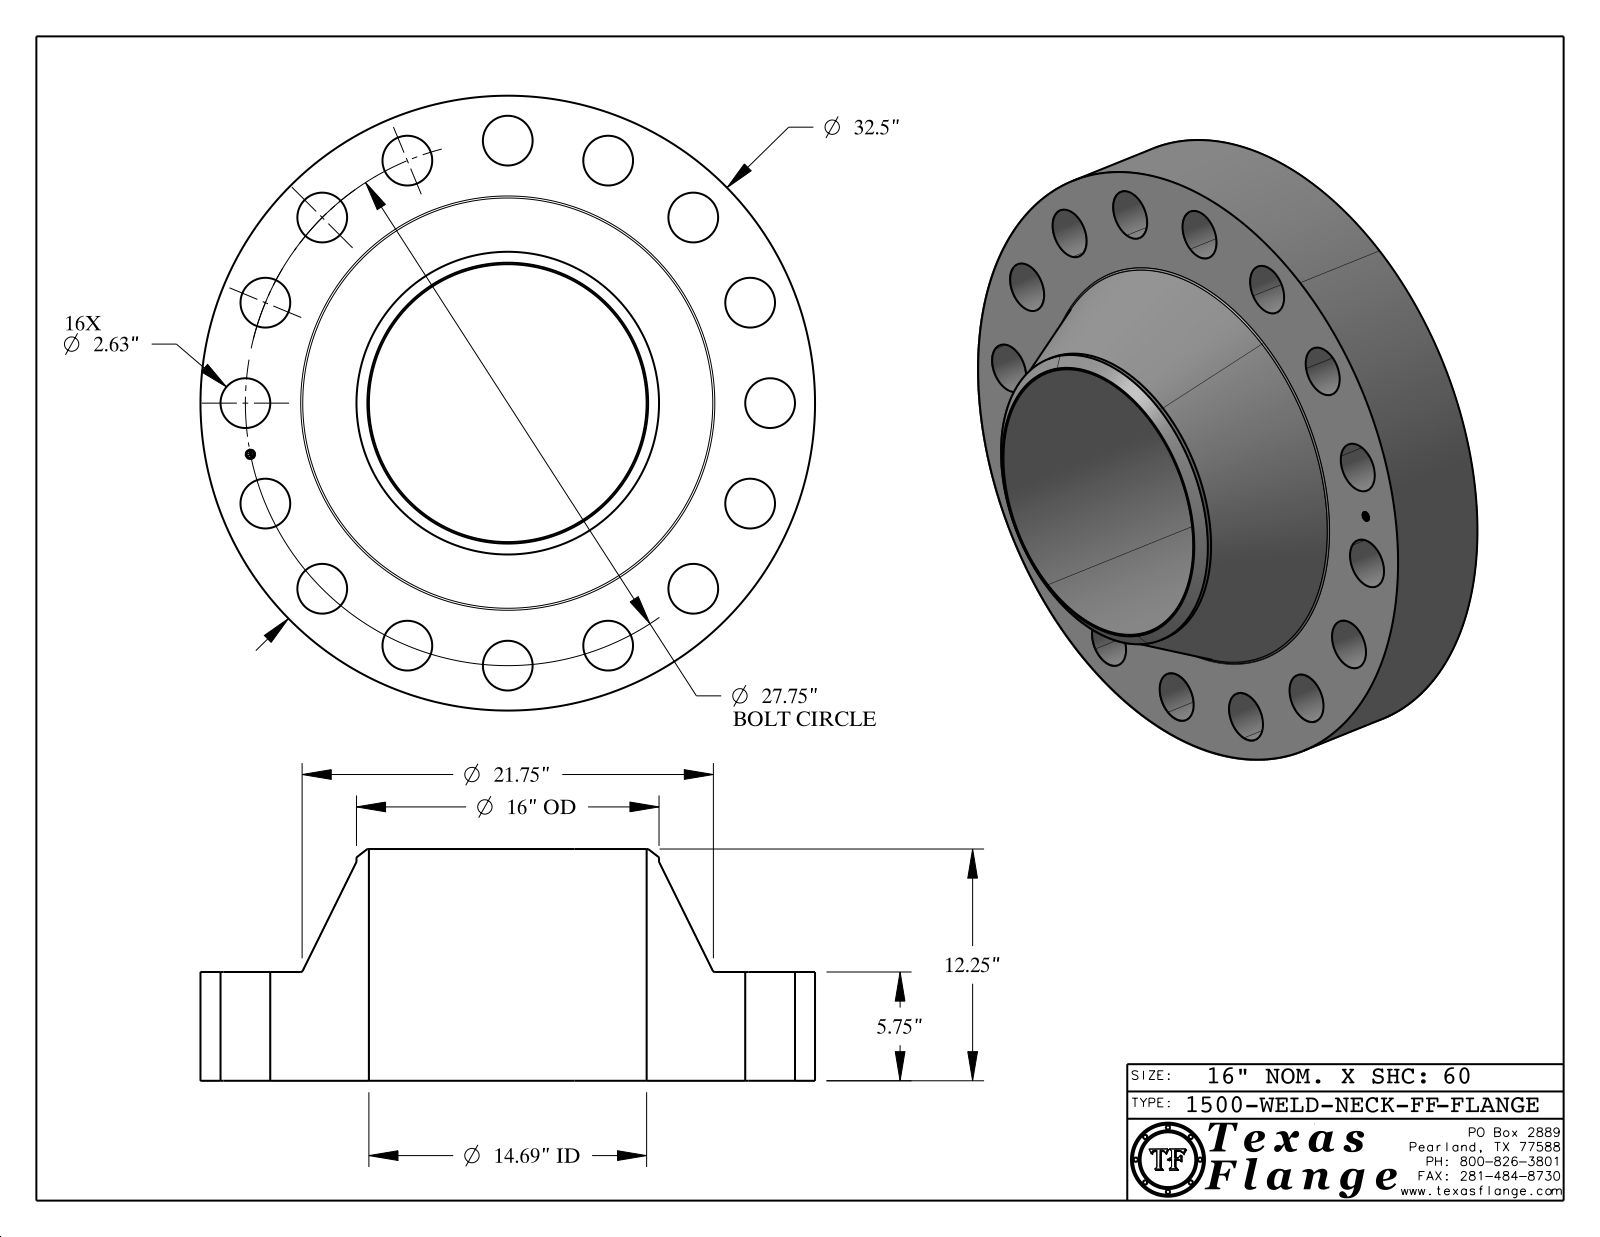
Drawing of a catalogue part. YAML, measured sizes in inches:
part_name: "1500-WELD-NECK-FF"
step_written_by: "CATIA V5 STEP AP214 (AUTOMOTIVE_DESIGN)"
units: inches
bodies: {solids: 1, faces: 432, planar: 368, cylindrical: 58, other: 6}
overall_size: [32.5, 32.5, 12.25]
volume: 3966
surface_area: 3292
round_holes:
  - {diameter: 2.63, count: 16}
  - {diameter: 0.495, count: 1}
  - {diameter: 14.688, count: 1}
round_bosses_or_shafts:
  - {diameter: 0.03, count: 8}
  - {diameter: 32.5, count: 1}
  - {diameter: 16, count: 1}
  - {diameter: 0.39, count: 1}
face_to_face_distances: [5.75, 12.25, 6.5, 0.015, 5.735, 6.515, 0.148, 0.145, 0.027, 0.096]
hole_center_spacings: [5.414, 15.417, 25.638, 27.217, 10.62, 13.875, 19.622, 23.073]
